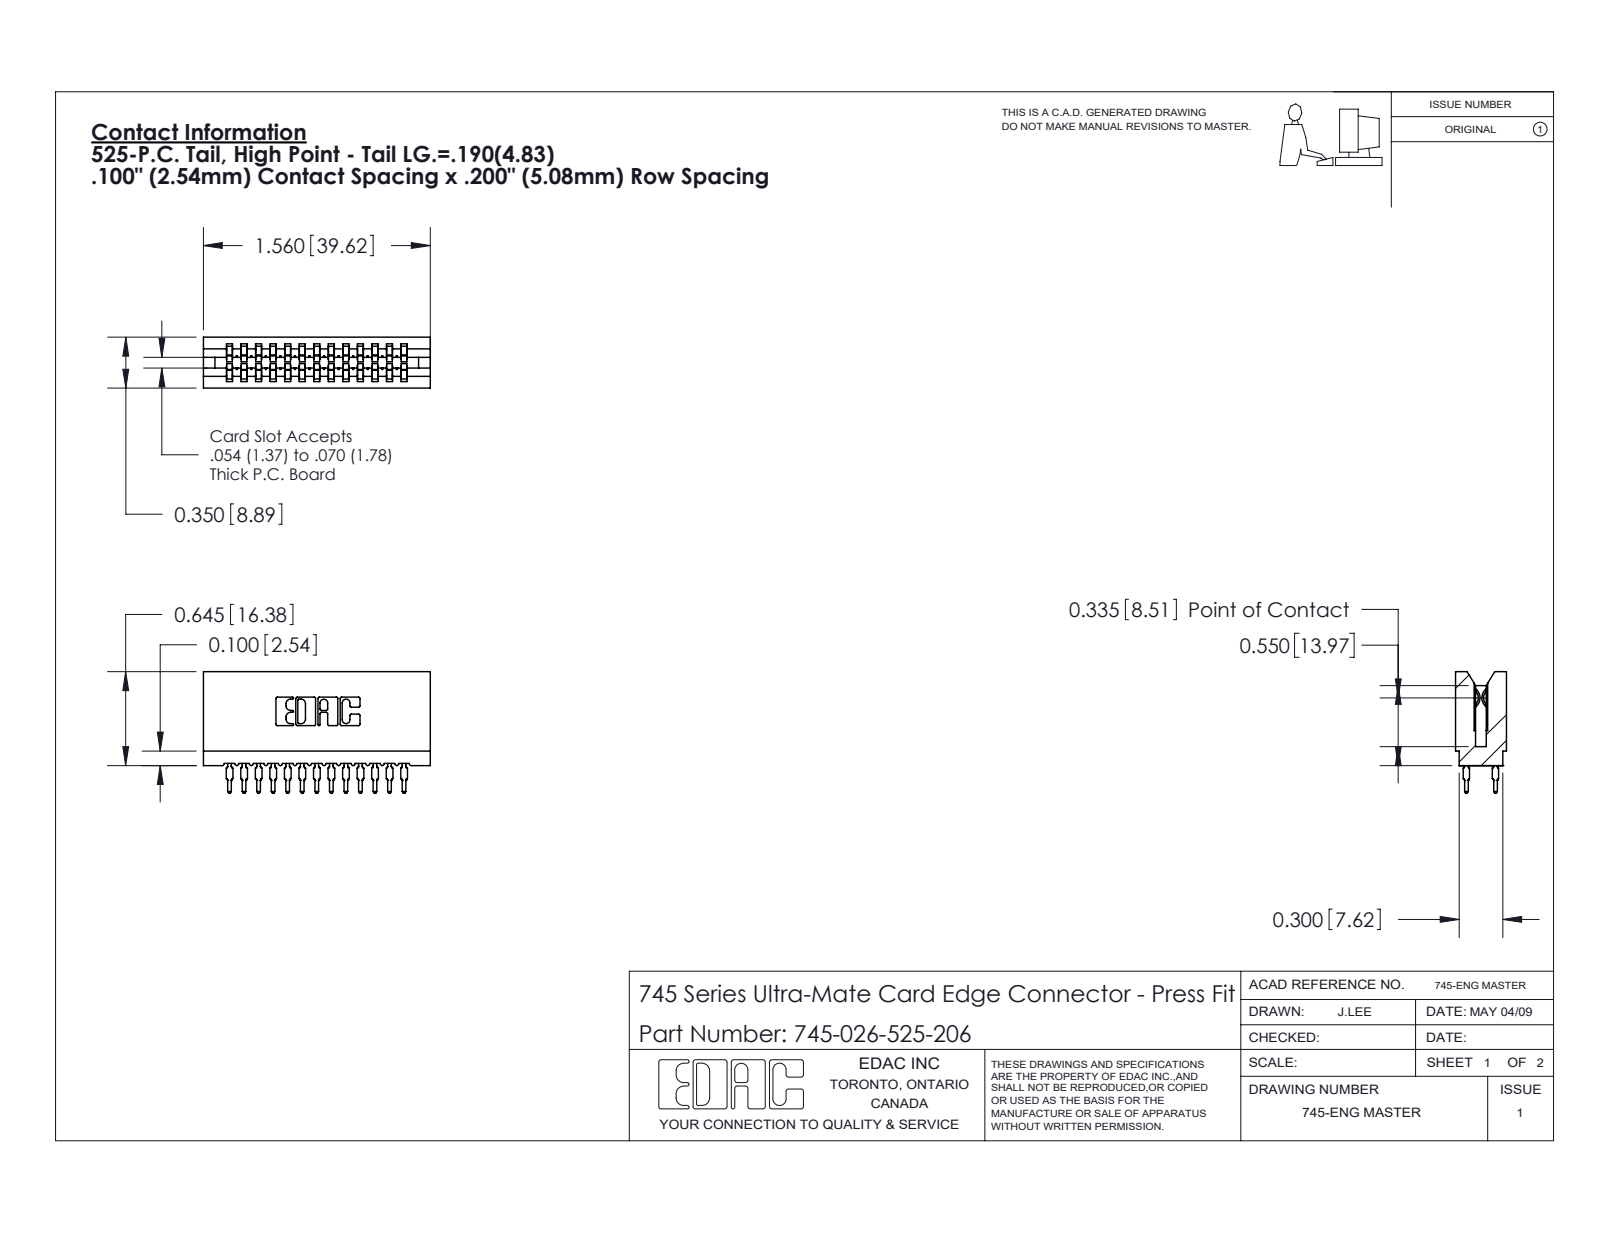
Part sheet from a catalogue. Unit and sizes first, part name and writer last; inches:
Units: inches
Overall size (bounding box): 1.56 × 0.836 × 0.35
Partial cylindrical surfaces — rounded edges, fillets, slot ends (radius × count): R0.021 ×52, R0.015 ×26, R0.01 ×22, R0.005 ×8, R0.011 ×8, R0.007 ×6, R0.031 ×6, R0.026 ×3
Main face-to-face distances: 0.1, 0.2, 0.3, 0.4, 0.35, 0.5, 0.058, 0.6, 0.358, 0.7
Volume: 0.227 in³ · Surface area: 10.67 in²
Bodies: 27 solids, 2423 faces (1252 planar, 495 cylindrical, 676 other)
Part name (STEP PRODUCT): 745 Part_Insulator Option - 06; 745-292-001_525; 745-026-525-206
STEP written by: SolidWorks 2020 (CONFIG_CONTROL_DESIGN)
